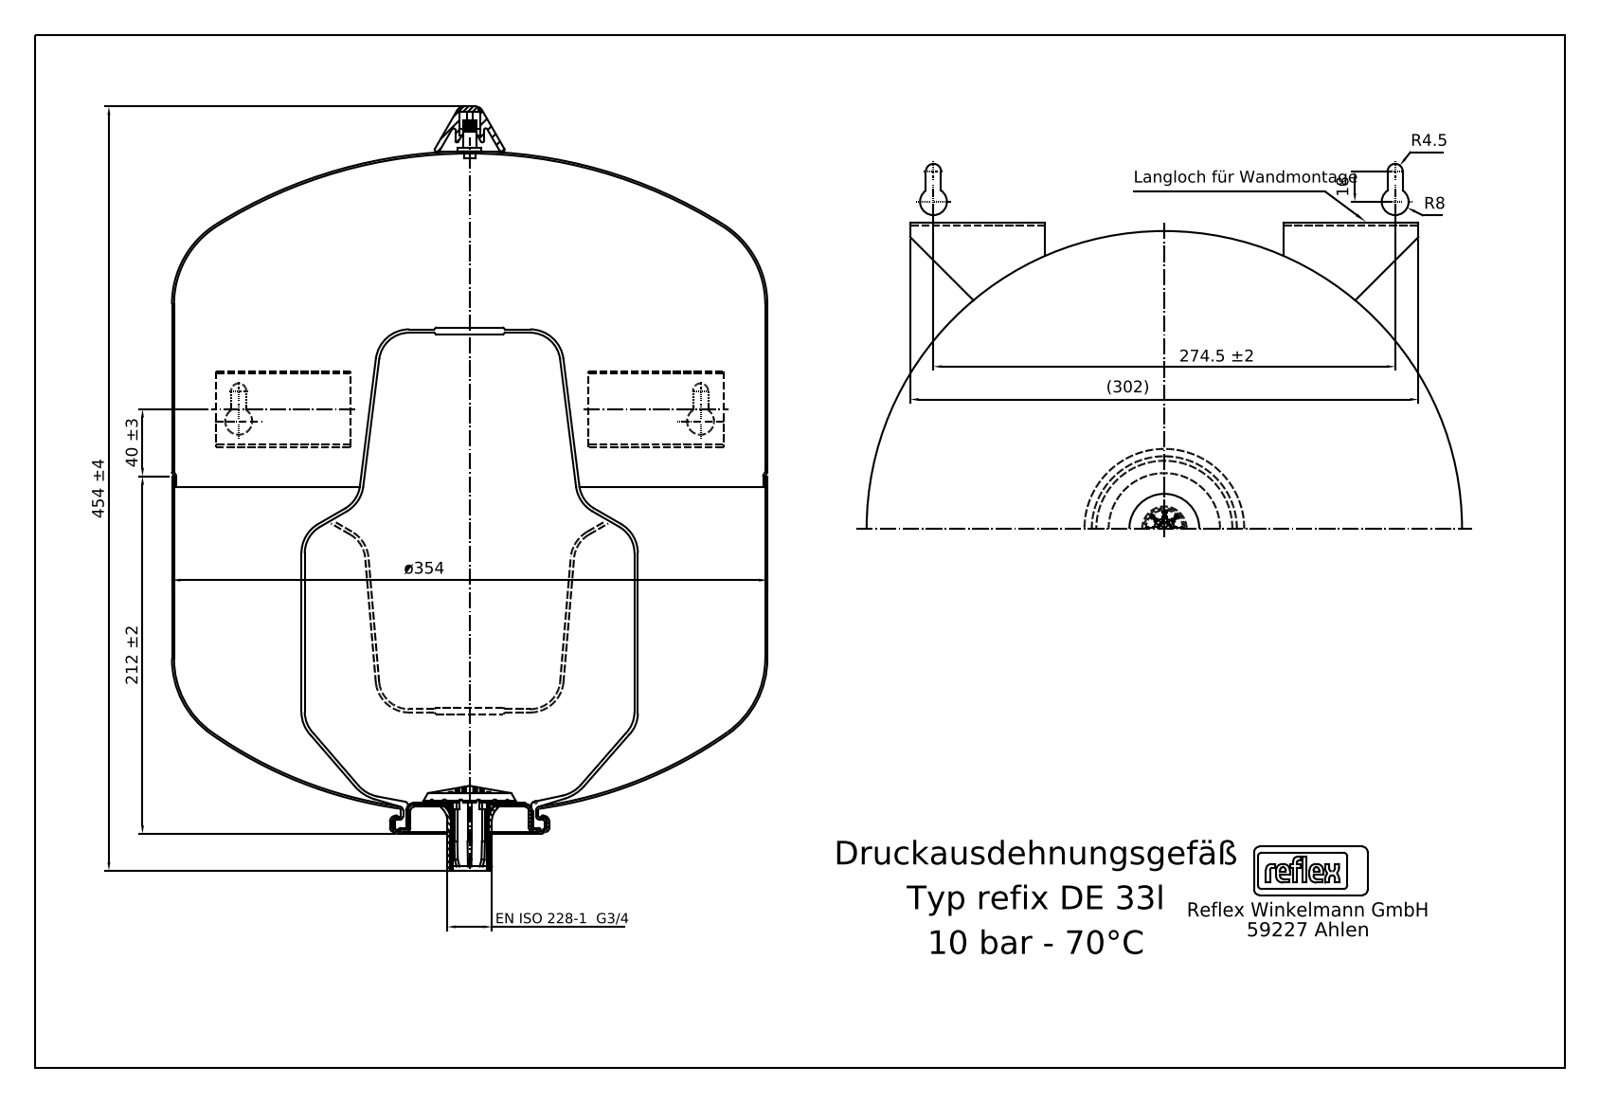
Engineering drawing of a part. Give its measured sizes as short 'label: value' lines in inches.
written by: Mechanical Desktop 2011 (CONFIG_CONTROL_DESIGN)
unit: in
bodies: 16 solids, 276 faces (124 planar, 102 cylindrical, 50 other)
size: 17.992 × 14.198 × 13.937
volume: 1 986 in³; area: 1 526 in²
holes: 1× ⌀0.555, 1× ⌀0.63, 1× ⌀0.744
bosses: 1× ⌀13.937, 1× ⌀3.78, 1× ⌀3.228, 1× ⌀1.059, 1× ⌀0.673, 1× ⌀0.354, 1× ⌀0.236
rounds: 4× R0.074, 4× R0.11, 4× R0.116, 4× R0.197, 4× R0.199, 2× R0.075, 2× R0.098, 2× R0.11
face distances: 8.346, 0.079, 3.307, 11.654, 0.512, 3.819, 12.165, 1.693, 0.02, 0.354
